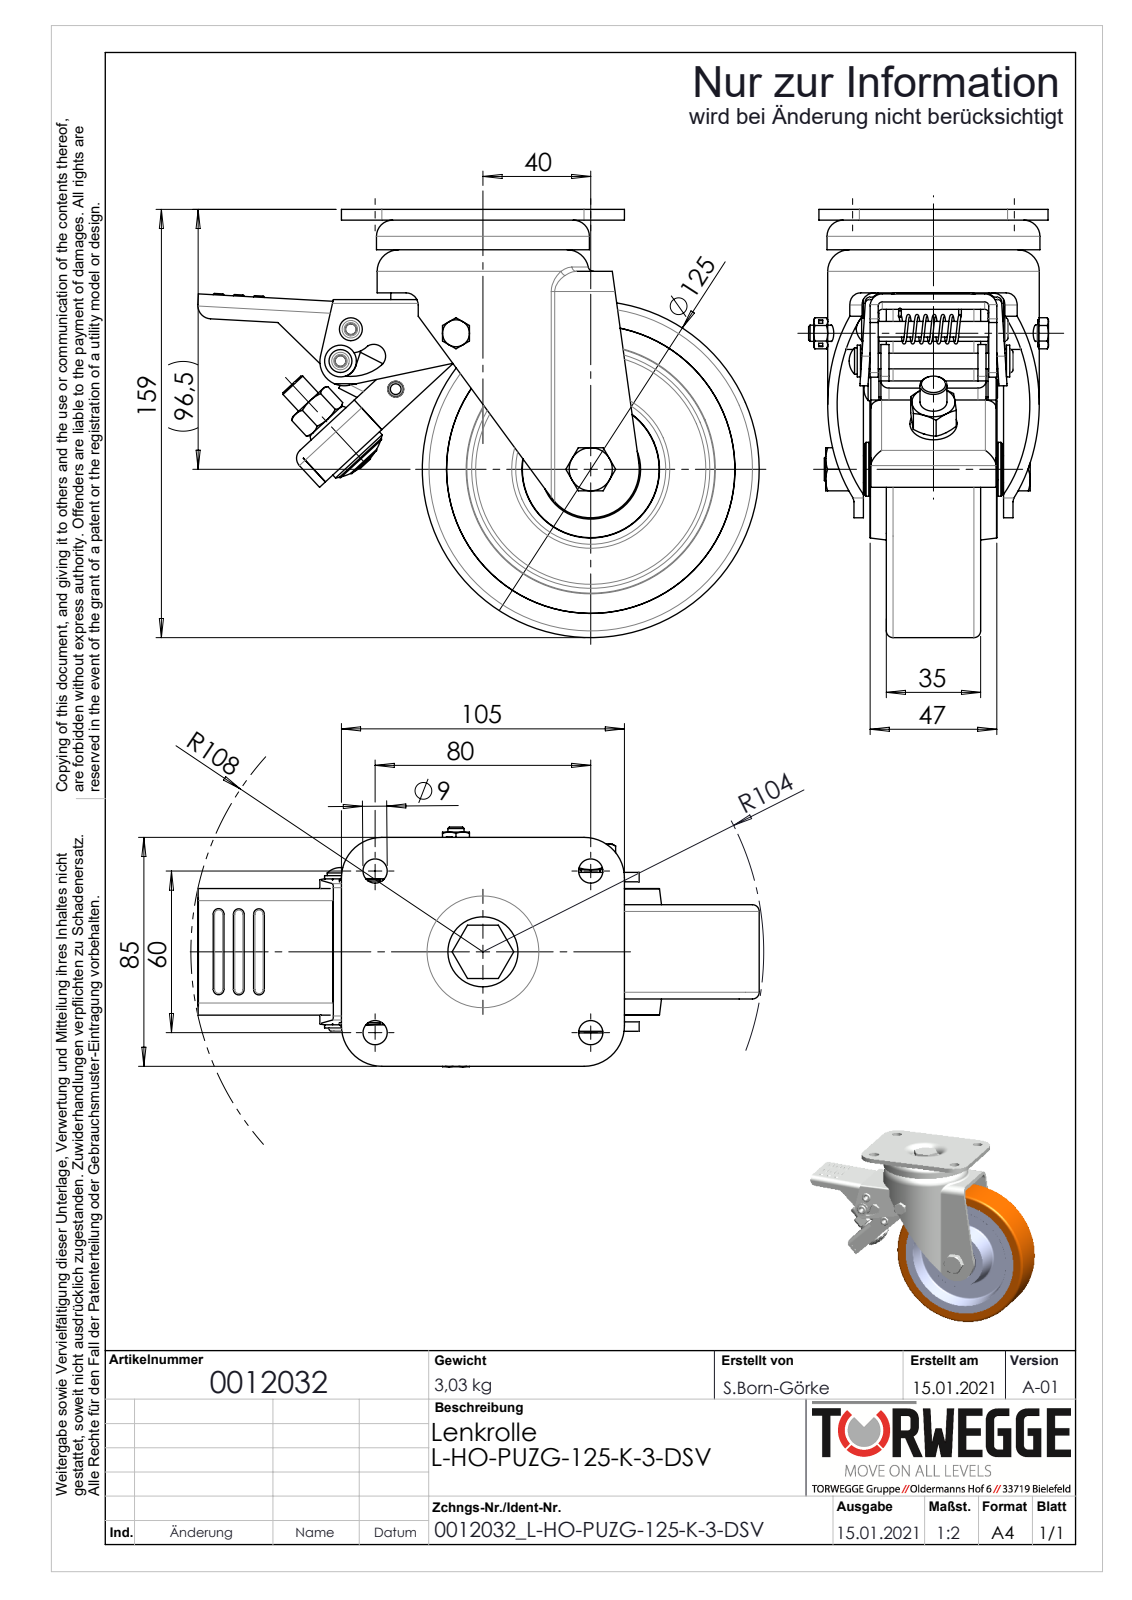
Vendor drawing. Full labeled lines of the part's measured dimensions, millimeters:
Part name (STEP PRODUCT): 0012032
STEP written by: SolidWorks 2018 (AUTOMOTIVE_DESIGN)
Units: millimetres
Bodies: 0 solids, 906 faces (290 planar, 282 cylindrical, 334 other)
Overall size (bounding box): 208.29 × 159 × 89
Round holes (diameter × count): ⌀6 ×4, ⌀9 ×4, ⌀1 ×2, ⌀8.5 ×2, ⌀10 ×2, ⌀16 ×2, ⌀4 ×1, ⌀5 ×1, ⌀5.8 ×1, ⌀6.2 ×1, ⌀6.3 ×1, ⌀8 ×1
Round bosses / shafts (diameter × count): ⌀12 ×2, ⌀125 ×1, ⌀79 ×1, ⌀23.6 ×1, ⌀20 ×1, ⌀18 ×1, ⌀11.8 ×1, ⌀10 ×1
Partial cylindrical surfaces — rounded edges, fillets, slot ends (radius × count): R1.5 ×16, R0.5 ×6, R4 ×5, R1 ×4, R15 ×4, R4.5 ×3, R7.5 ×3, R2 ×2
Main face-to-face distances: 3, 15, 6, 3.5, 11, 29.5, 43.5, 47, 4, 14
Hole centre spacings: 50, 60, 80, 100, 12.42, 23, 27.78, 30.5
